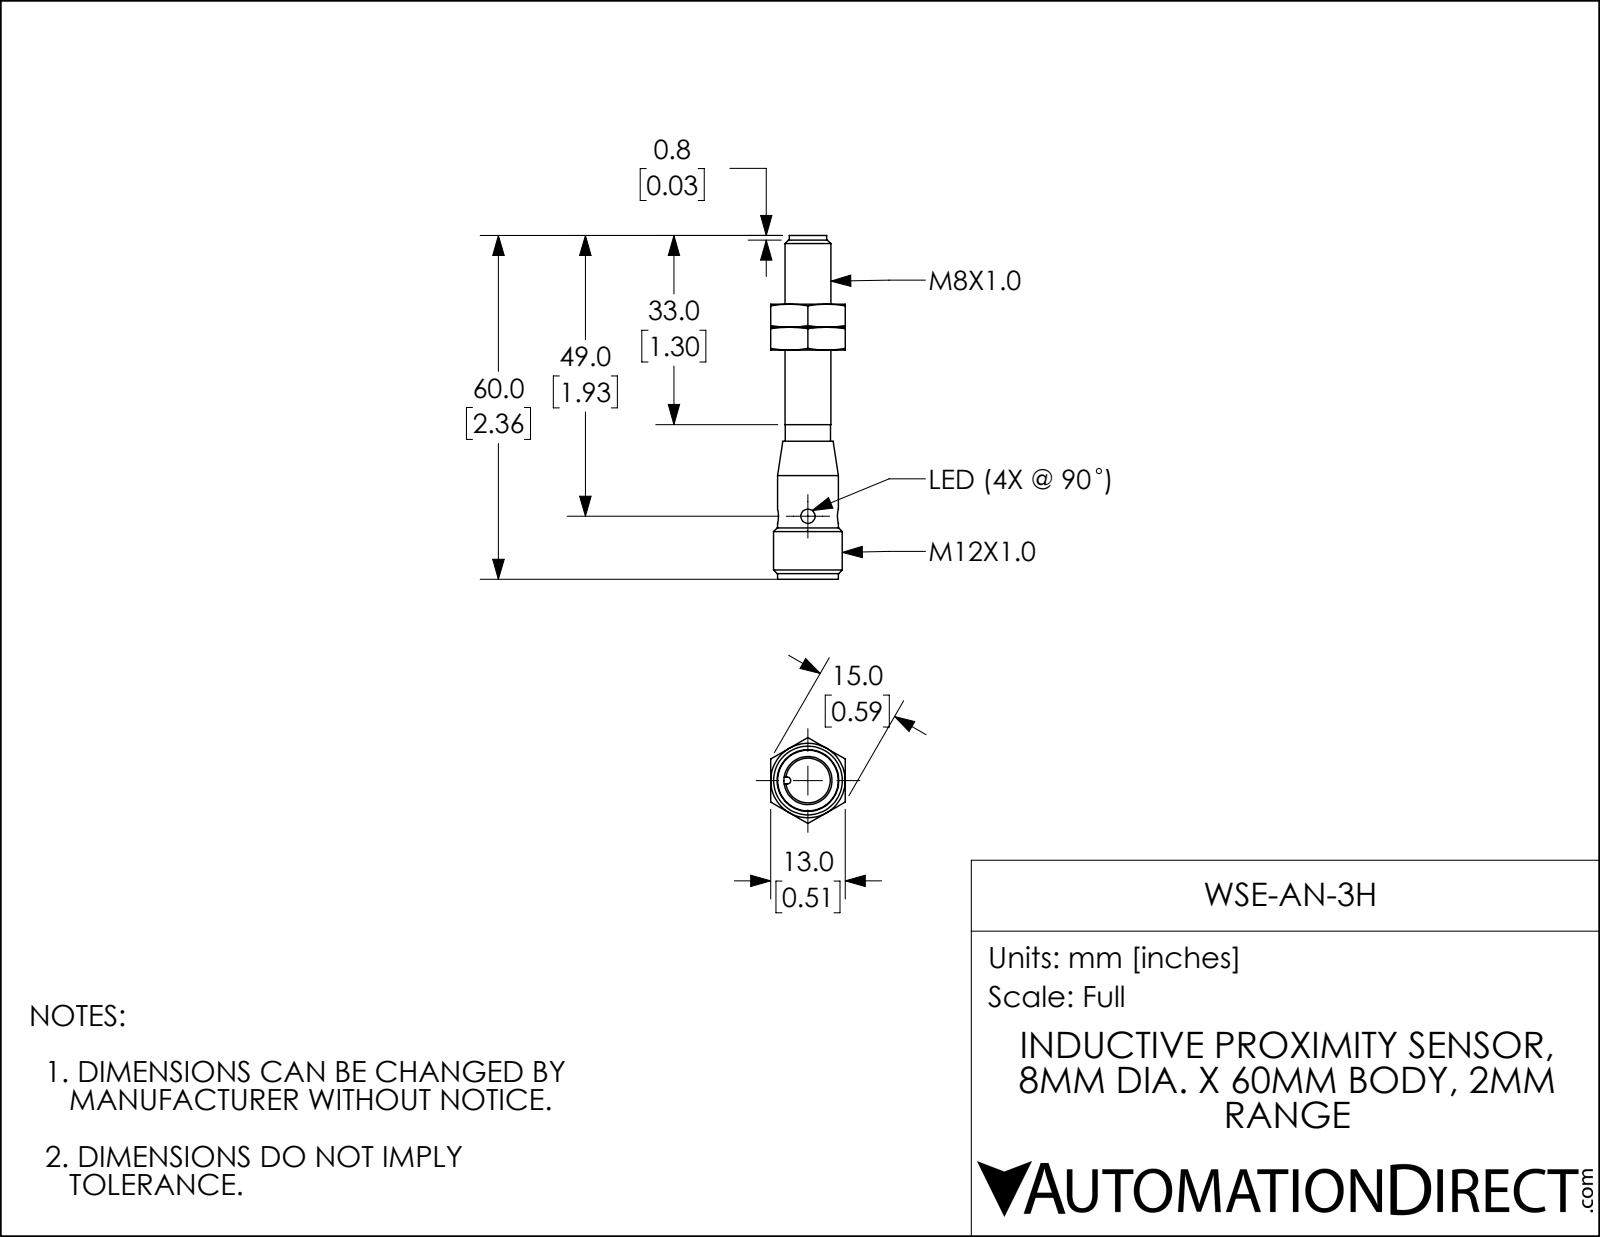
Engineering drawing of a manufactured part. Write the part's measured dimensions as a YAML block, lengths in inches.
part_name: "WSE-AN-3H"
step_written_by: "SolidWorks 2017 (AUTOMOTIVE_DESIGN)"
units: inches
bodies: {solids: 3, faces: 78, planar: 27, cylindrical: 14, other: 37}
overall_size: [2.362, 0.591, 0.512]
volume: 0.267
surface_area: 4.763
round_holes:
  - {diameter: 0.098, count: 2}
  - {diameter: 0.272, count: 1}
  - {diameter: 0.331, count: 1}
round_bosses_or_shafts:
  - {diameter: 0.472, count: 1}
  - {diameter: 0.417, count: 1}
  - {diameter: 0.315, count: 1}
  - {diameter: 0.311, count: 1}
  - {diameter: 0.258, count: 1}
partial_cylinders:
  - {radius: 0.024, count: 1}
face_to_face_distances: [0.512, 0.157, 0.315, 1.382, 1.224, 1.539, 2.012, 0.787, 0.63, 0.472]
